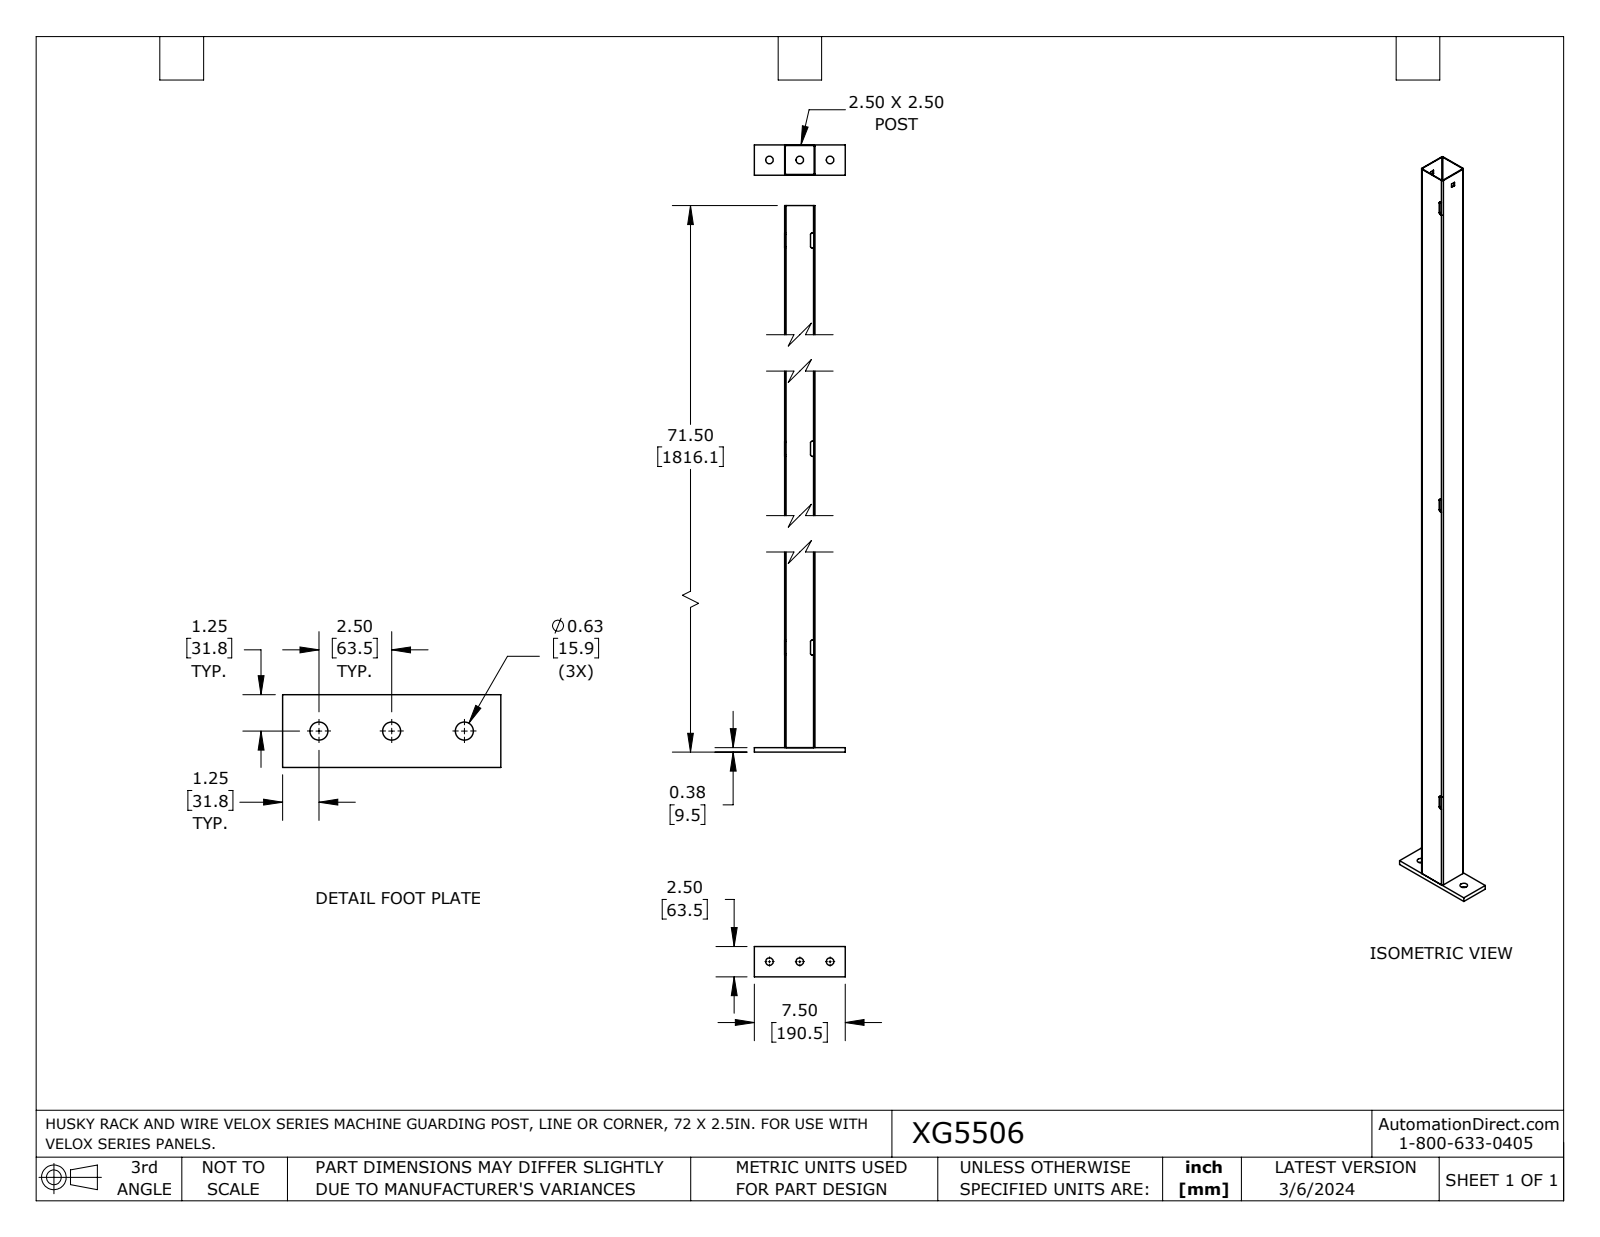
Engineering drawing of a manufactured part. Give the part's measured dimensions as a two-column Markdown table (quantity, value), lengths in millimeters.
| quantity | value |
| --- | --- |
| part name | XG5506_Default |
| STEP written by | SolidWorks 2023 (CONFIG_CONTROL_DESIGN) |
| units | millimeters |
| bodies | 2 solids, 107 faces (72 planar, 35 cylindrical, 0 other) |
| overall size | 1816.1 × 190.5 × 63.5 |
| volume | 755 400 mm³ |
| surface area | 908 400 mm² |
| round holes (diameter × count) | 15.9 × 3 |
| partial cylindrical surfaces (radius × count) | 3.3 × 18, 1.6 × 4, 3 × 4 |
| main face-to-face distances | 1.5, 62, 63.5, 60.6, 9.5, 65, 125.5, 127, 190.5, 2.5 |
| hole center spacings | 63.5, 127 |
